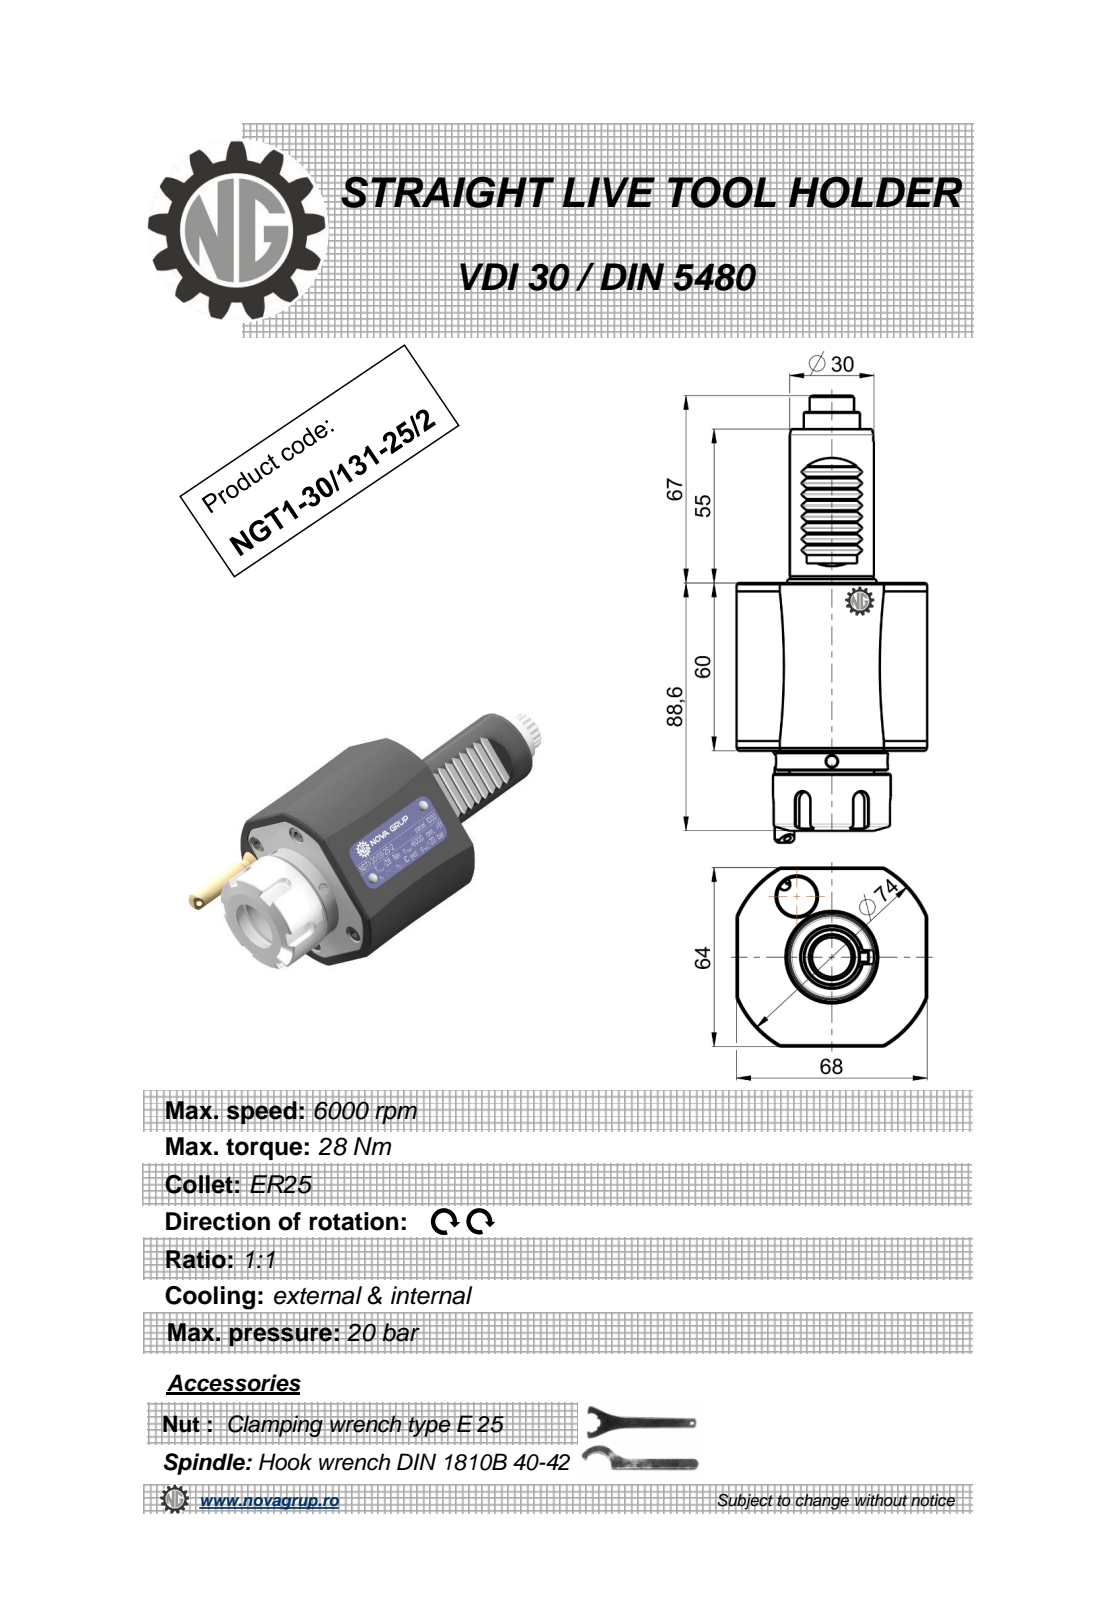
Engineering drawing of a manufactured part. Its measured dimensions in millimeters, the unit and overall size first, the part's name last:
Units: millimetres
Overall size (bounding box): 159.83 × 68 × 65.6
Round holes (diameter × count): ⌀4 ×2, ⌀2.5 ×1, ⌀3 ×1, ⌀20.3 ×1
Round bosses / shafts (diameter × count): ⌀42 ×1, ⌀40 ×1, ⌀33 ×1, ⌀30 ×1, ⌀20 ×1, ⌀9 ×1, ⌀7 ×1, ⌀5 ×1
Partial cylindrical surfaces — rounded edges, fillets, slot ends (radius × count): R1.98 ×36, R0.3 ×8, R3 ×5, R7.08 ×1, R7.92 ×1, R13 ×1, R37 ×1
Main face-to-face distances: 60, 64, 68, 67, 83.7, 23.7, 2.83, 68.1, 8.1, 15.6
Hole centre spacings: 31
Volume: 308 239 mm³ · Surface area: 34 881 mm²
Bodies: 1 solid, 342 faces (99 planar, 132 cylindrical, 111 other)
Part name (STEP PRODUCT): NGT1_30_131_25_1
STEP written by: PRO/ENGINEER BY PARAMETRIC TECHNOLOGY CORPORATION, 2010280 (CONFIG_CONTROL_DESIGN)
